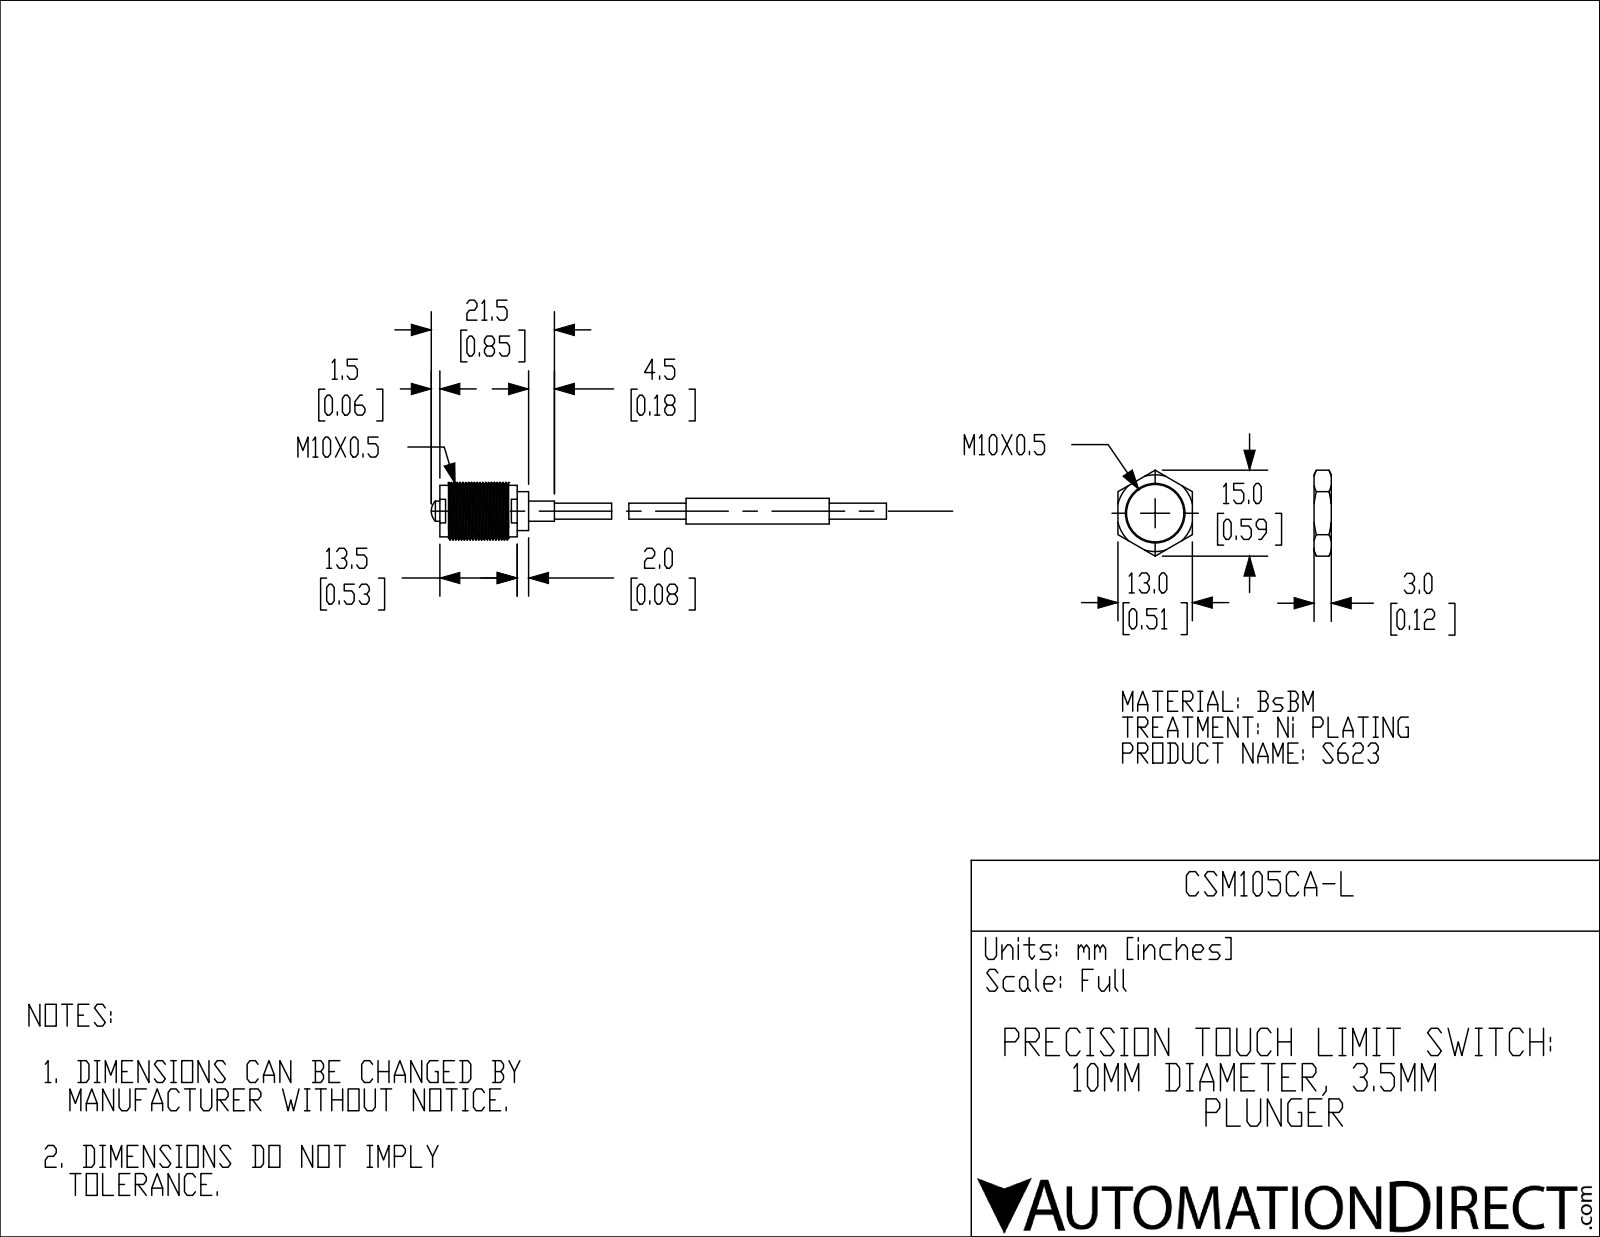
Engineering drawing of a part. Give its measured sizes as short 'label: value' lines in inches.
name: CSM105CA-L
written by: SolidWorks 2018 (AUTOMOTIVE_DESIGN)
unit: in
bodies: 2 solids, 32 faces (19 planar, 10 cylindrical, 3 other)
size: 3.13 × 0.394 × 0.394
volume: 0.105 in³; area: 2.043 in²
bosses: 1× ⌀0.394, 1× ⌀0.354, 1× ⌀0.268, 1× ⌀0.177, 1× ⌀0.138, 1× ⌀0.11
face distances: 0.61, 0.531, 0.079, 0.059, 0.472, 0.394, 1.378, 0.315, 0.551, 0.413
